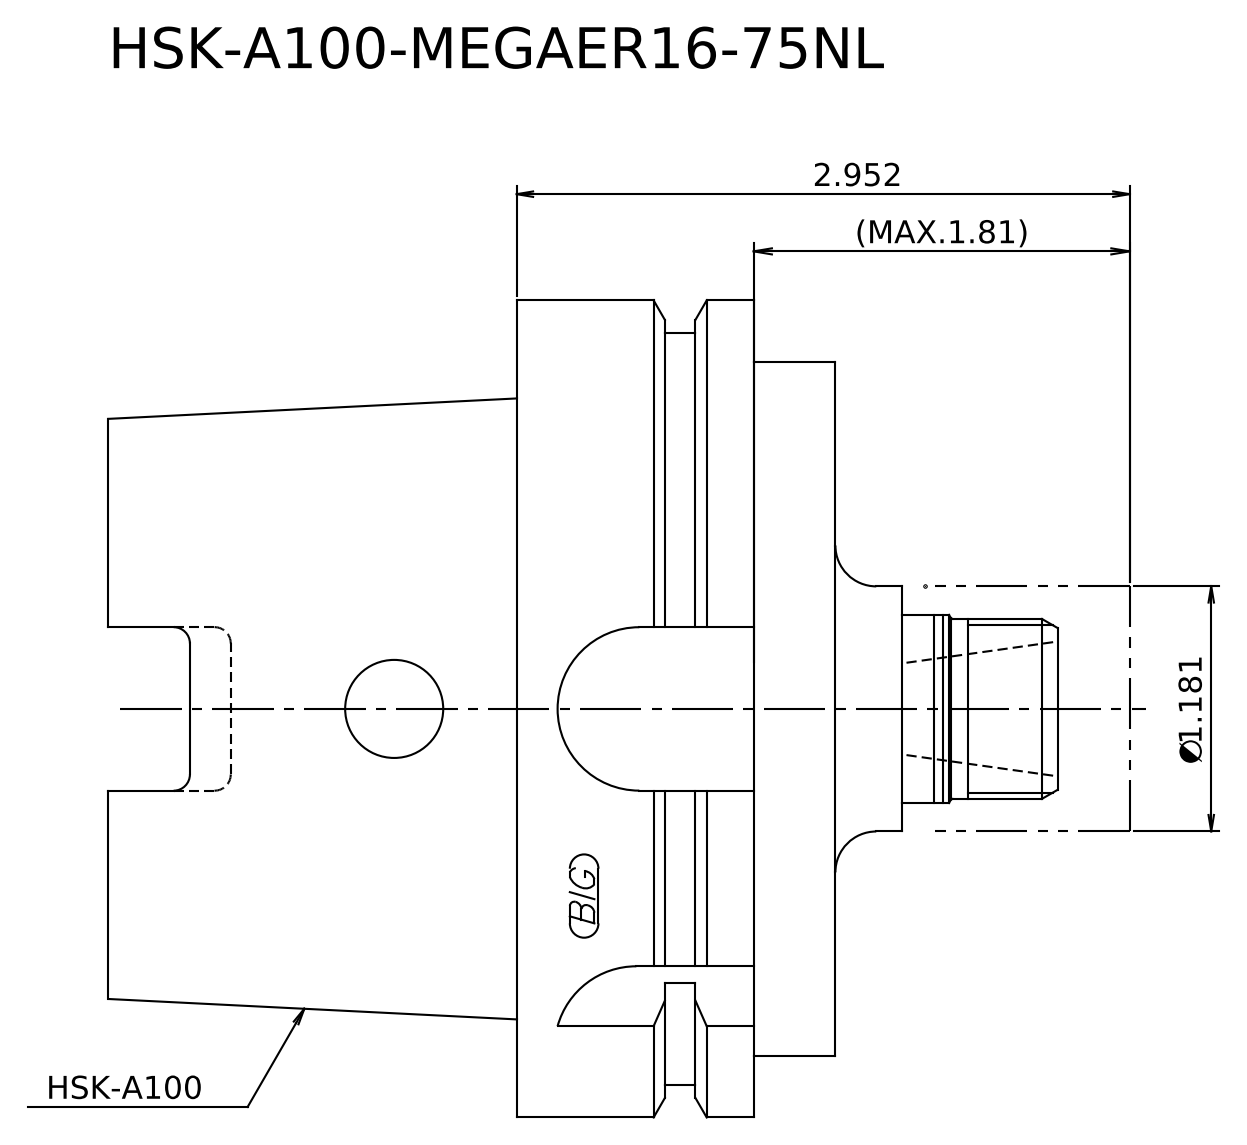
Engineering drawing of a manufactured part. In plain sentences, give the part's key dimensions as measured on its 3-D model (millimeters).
Its 3-D file was written by "Kubotek KeyCreator 2011 V10.0.2 (22737) (automotive_design)". It is 2 solids with 24 faces: 10 planar, 8 cylindrical and 6 other. Overall it measures 125 by 100 by 100 millimeters. Its volume is 523 316 cubic millimeters and its surface area 45 702 square millimeters. Round bosses or shafts: 1 of diameter 100, 1 of diameter 92, 1 of diameter 85, 1 of diameter 30, 1 of diameter 23, 1 of diameter 22. The main face-to-face distances are 50, 89, 39, 10, 29, 79, 11, 21, 100, 25.
